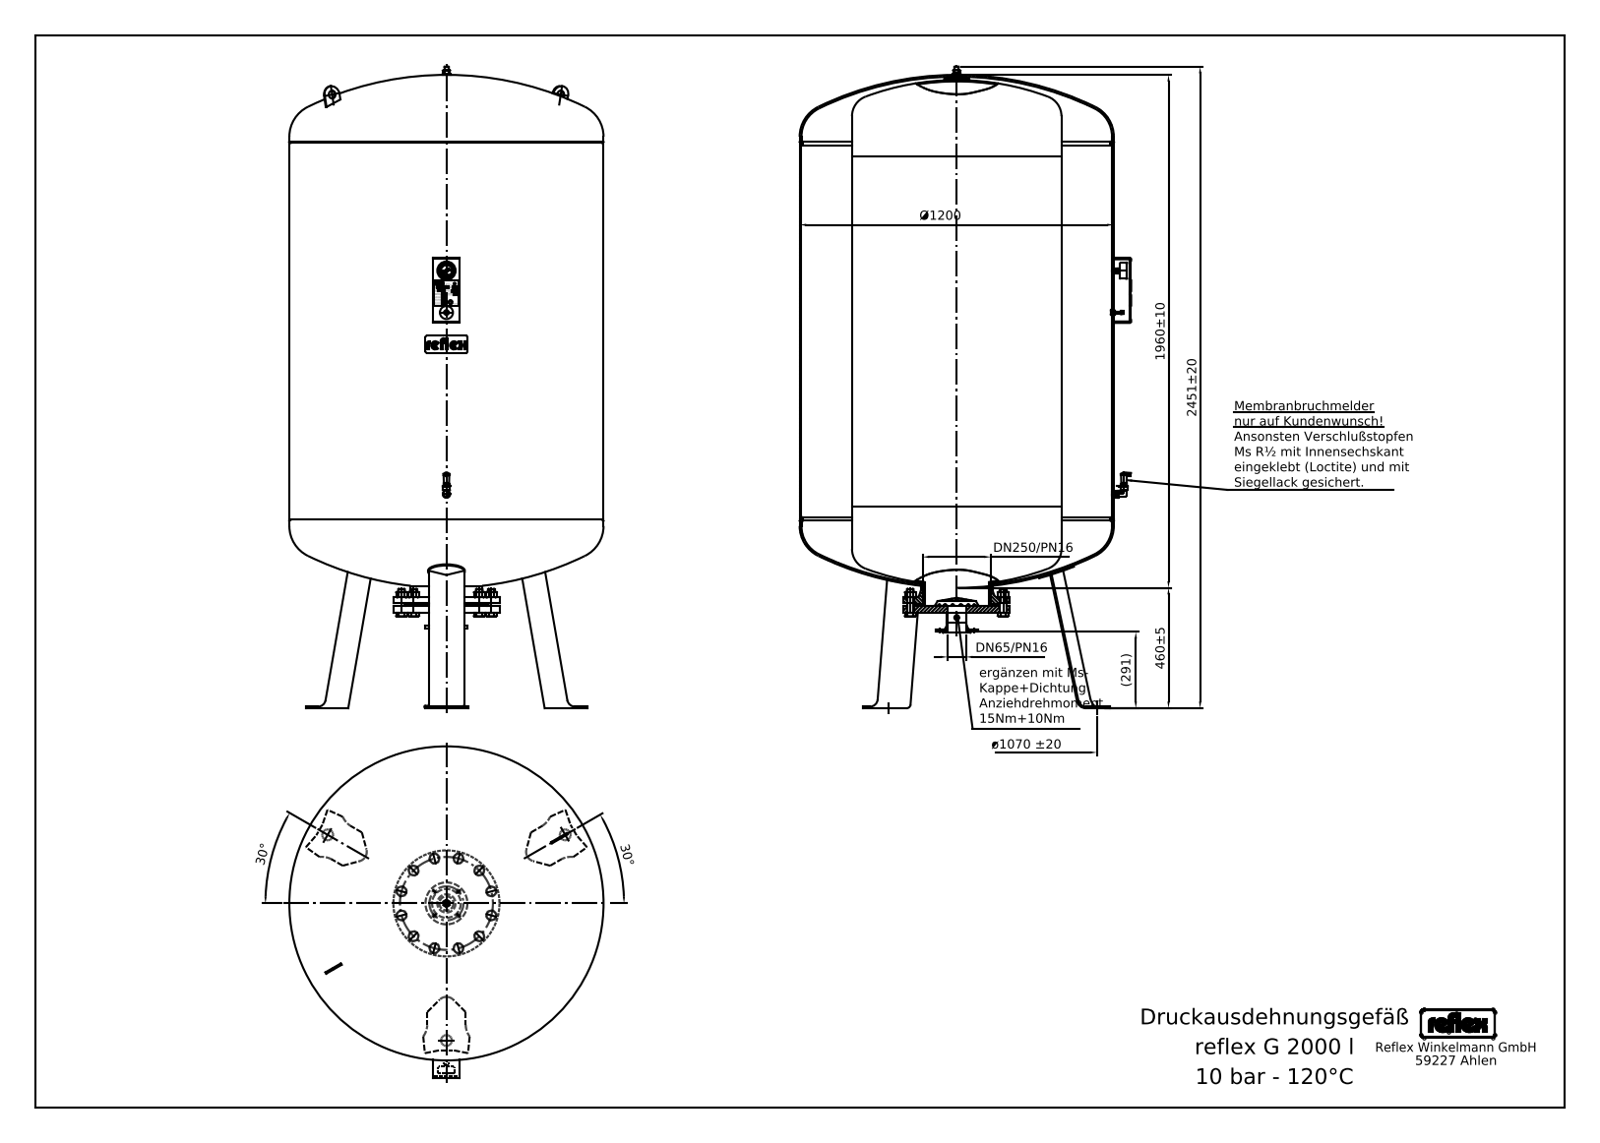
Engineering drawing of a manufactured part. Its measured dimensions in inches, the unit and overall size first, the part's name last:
Units: inches
Overall size (bounding box): 96.457 × 49.843 × 47.34
Round holes (diameter × count): ⌀0.394 ×1, ⌀1.181 ×1, ⌀1.969 ×1, ⌀2.717 ×1, ⌀10.252 ×1
Round bosses / shafts (diameter × count): ⌀0.63 ×13, ⌀1.102 ×2, ⌀1.024 ×2, ⌀0.787 ×2, ⌀47.244 ×1, ⌀15.945 ×1, ⌀10.748 ×1, ⌀2.996 ×1
Partial cylindrical surfaces — rounded edges, fillets, slot ends (radius × count): R0.984 ×18, R0.332 ×4, R0.133 ×3, R0.354 ×3, R0.039 ×2, R0.197 ×2, R0.227 ×2, R0.394 ×2
Main face-to-face distances: 57.087, 1.024, 12.283, 69.37, 13.307, 70.394, 1.22, 0.232, 0.235, 2.244
Hole centre spacings: 3.241, 24.232
Volume: 124 700 in³ · Surface area: 22 830 in²
Bodies: 23 solids, 612 faces (340 planar, 155 cylindrical, 117 other)
STEP written by: Mechanical Desktop 2008 (CONFIG_CONTROL_DESIGN)
